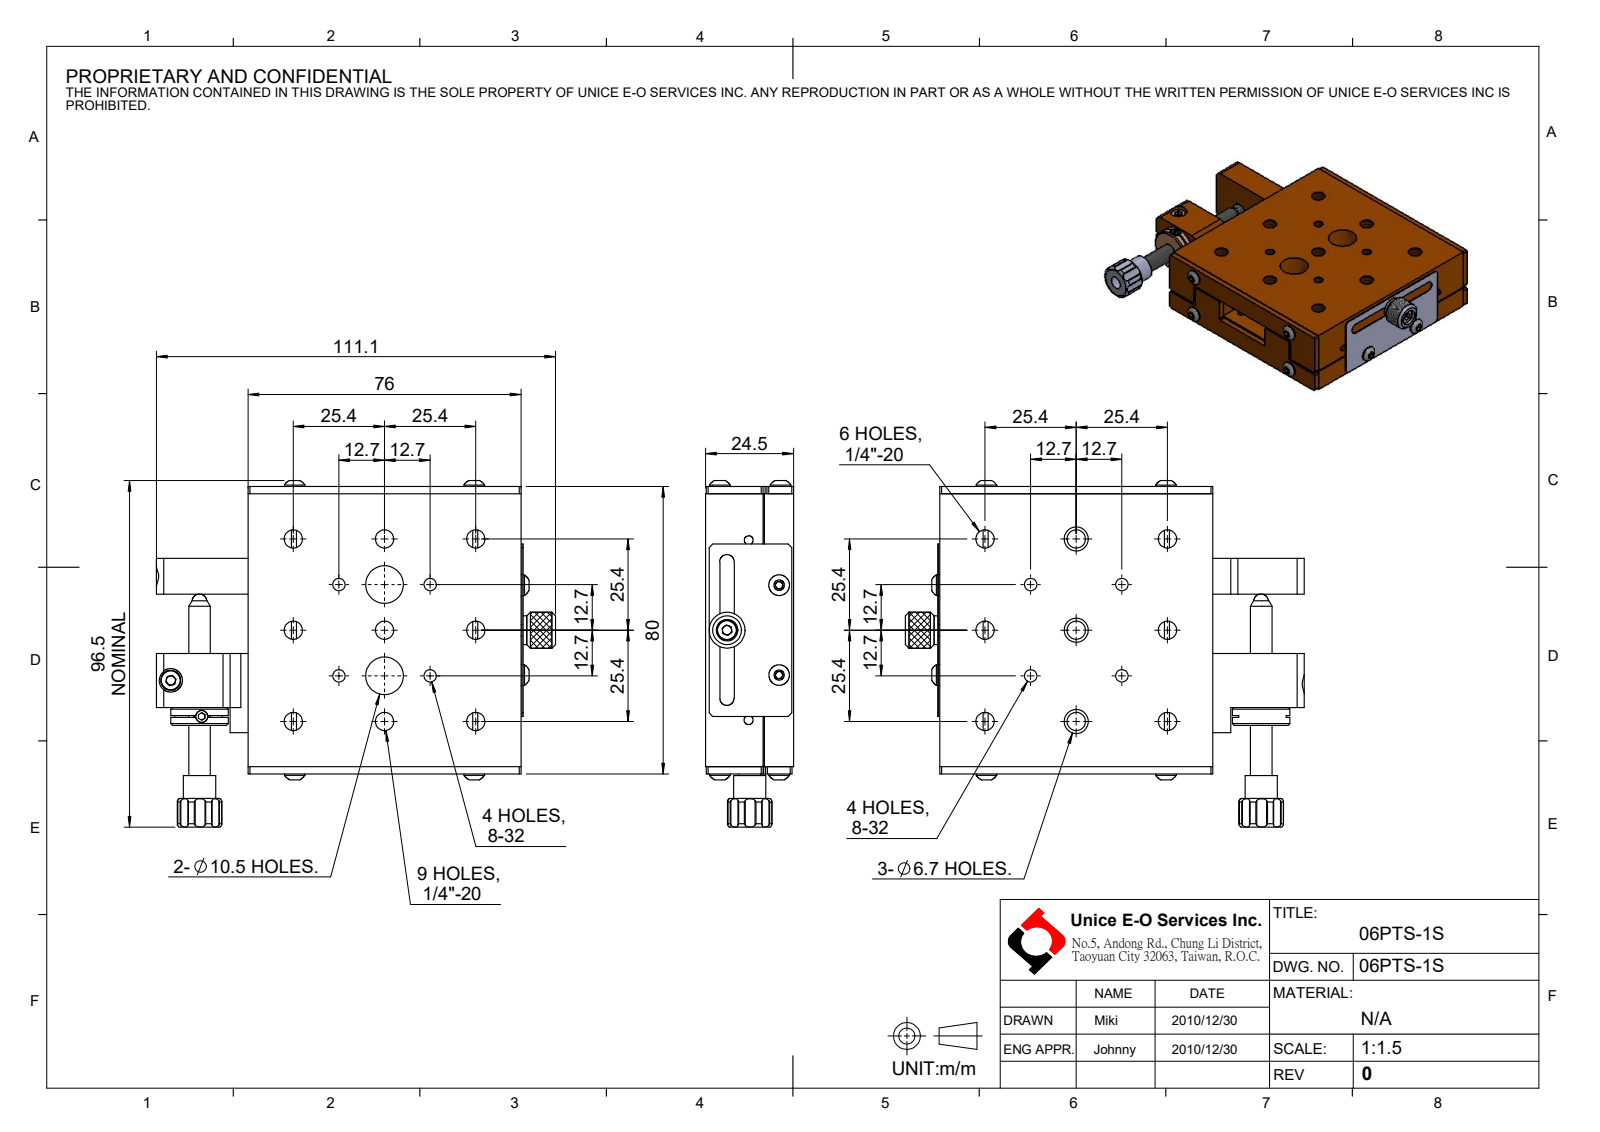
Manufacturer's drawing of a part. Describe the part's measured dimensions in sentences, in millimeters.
The part is named "06PTS-1S". Its 3-D file was written by "SolidWorks 2016 (CONFIG_CONTROL_DESIGN)". It is 39 solids with 1901 faces: 511 planar, 674 cylindrical and 716 other. Overall it measures 111.1 by 96.48 by 24.5 millimeters. Its volume is 133 428 cubic millimeters and its surface area 74 132 square millimeters. Round holes: 39 of diameter 2.5, 14 of diameter 3.5, 14 of diameter 6, 10 of diameter 4.5, 9 of diameter 3.3, 9 of diameter 5.11, 4 of diameter 3.4, 4 of diameter 3.45, 4 of diameter 6.5, 3 of diameter 6.7, 2 of diameter 3.2, 2 of diameter 10.5. Round bosses or shafts: 12 of diameter 3, 8 of diameter 5.7, 5 of diameter 5.5, 3 of diameter 6, 1 of diameter 16, 1 of diameter 10, 1 of diameter 9, 1 of diameter 8. Partial cylindrical surfaces (rounded edges, fillets, slot ends): 32 of radius 0.5, 16 of radius 0.3, 8 of radius 2, 8 of radius 2.75, 1 of radius 3, 1 of radius 6.35. The main face-to-face distances are 8.2, 8, 8.3, 8.1, 16.4, 24.5, 16.5, 76, 16.3, 7.9. The hole center spacings are 25.4, 17.96, 40.16, 50, 10, 19.29, 20, 25.93.
